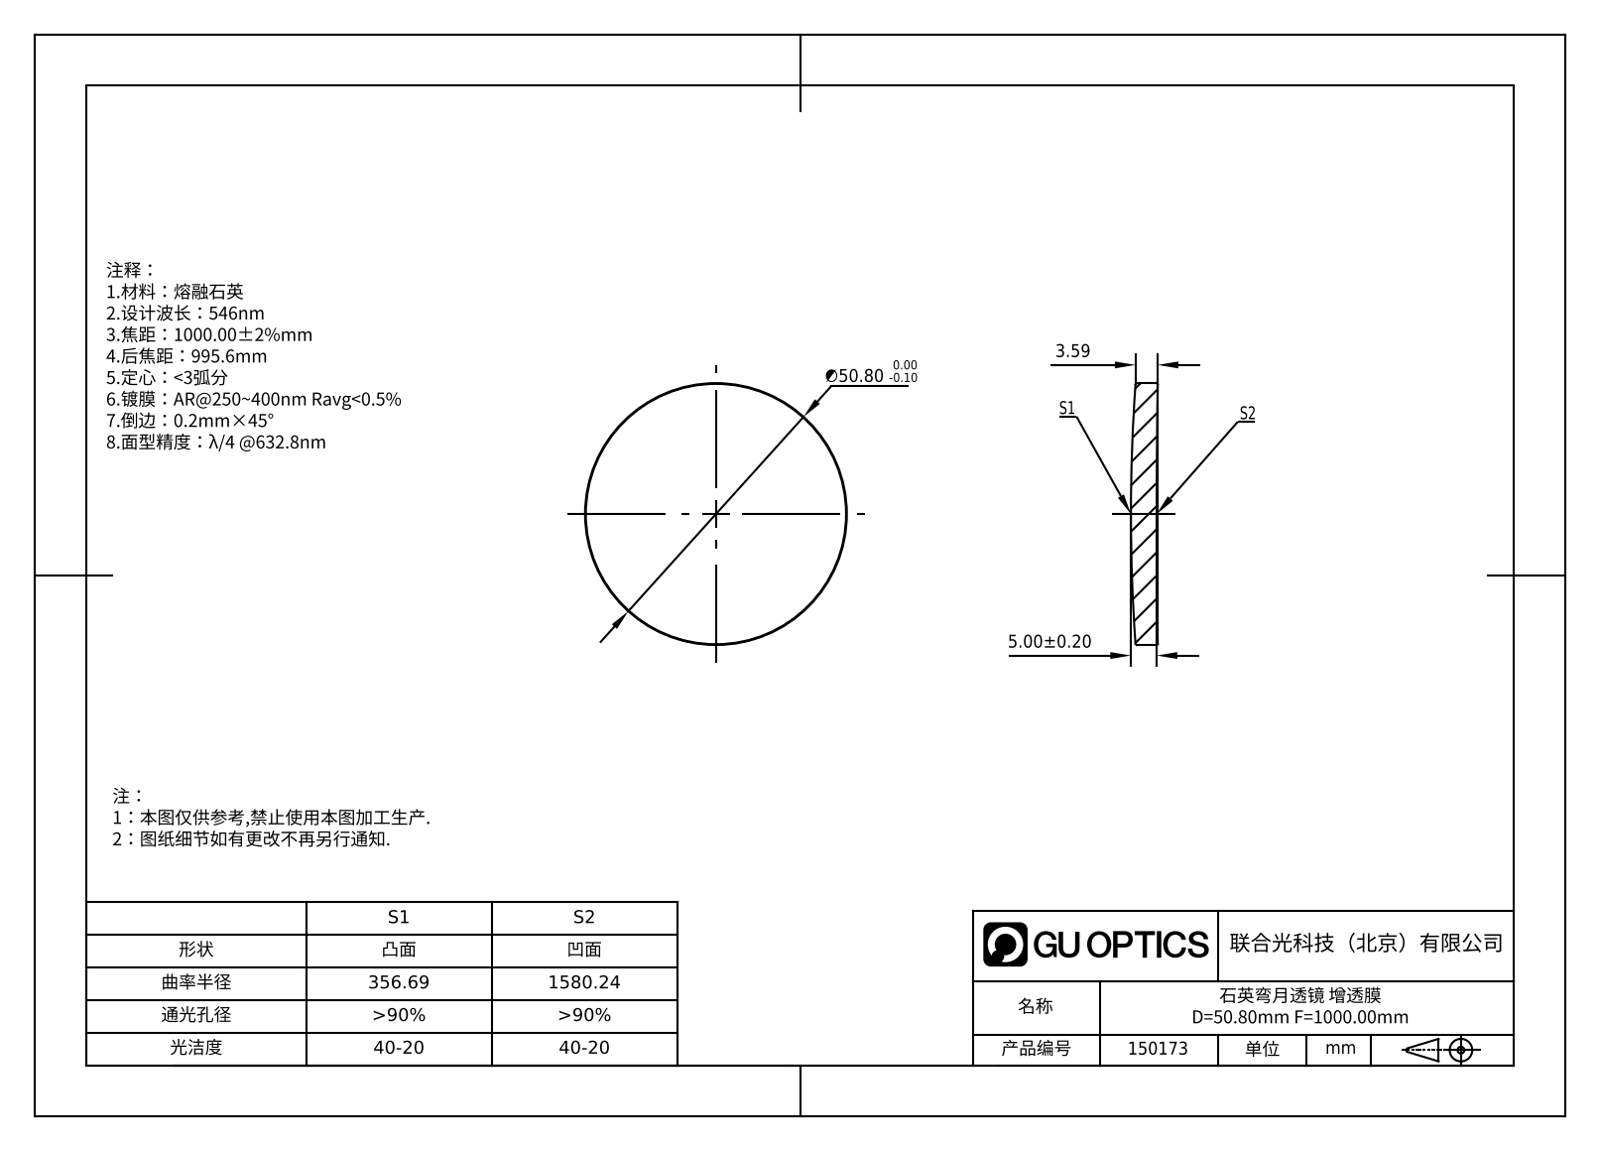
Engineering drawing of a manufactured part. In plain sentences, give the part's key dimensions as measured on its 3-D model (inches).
The part is named "GLM2-050B-1000-UV". Its 3-D file was written by "SolidWorks 2022 (AUTOMOTIVE_DESIGN)". It is 1 solid with 10 faces: 0 planar, 2 cylindrical and 8 other. Overall it measures 2 by 2 by 0.205 inches. Its volume is 0.575 cubic inches and its surface area 7.294 square inches. Round bosses or shafts: 1 of diameter 2.
